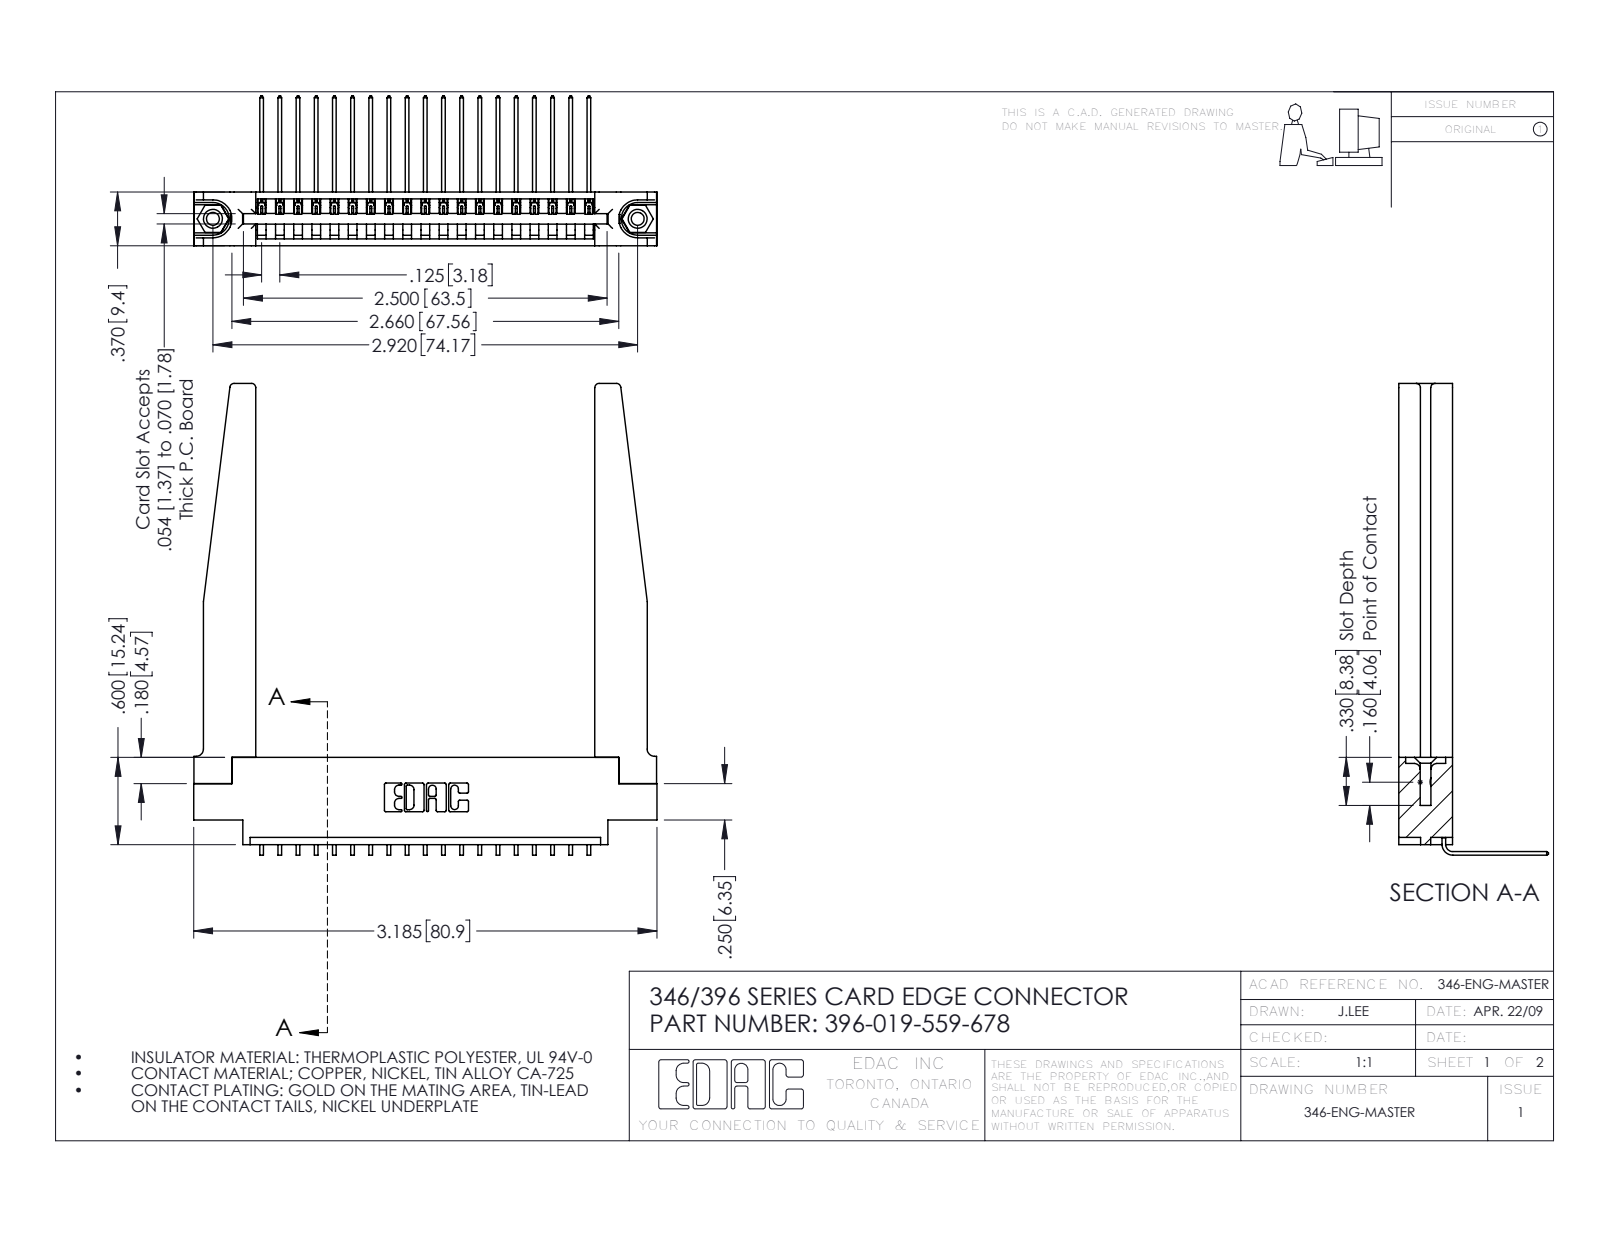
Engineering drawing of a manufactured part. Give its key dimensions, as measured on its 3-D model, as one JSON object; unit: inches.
{"part_name": "345-292-001_558 559 Tail - 1; 345-250-001_345-250-001-102; 396-019-559-678; 346-220-078_345-220-078 (+1 more)", "step_written_by": "SolidWorks 2016 (CONFIG_CONTROL_DESIGN)", "units": "inches", "bodies": {"solids": 24, "faces": 1500, "planar": 1020, "cylindrical": 428, "other": 52}, "overall_size": [3.243, 3.185, 1.03], "volume_in3": 0.879, "surface_area_in2": 25.1, "round_holes": [[0.089, 2], [0.125, 2], [0.156, 2], [0.064, 1]], "round_bosses_or_shafts": [[0.155, 2]], "partial_cylinders_radius": [[0.006, 38], [0.01, 22], [0.03, 8], [0.007, 6], [0.031, 6], [0.026, 3], [0.05, 3], [0.031, 2]], "face_to_face_distances": [0.37, 0.072, 0.048, 0.15, 0.148, 0.322, 0.25, 0.025, 0.102, 0.22], "hole_center_spacings": [0.246, 2.713, 2.92]}
